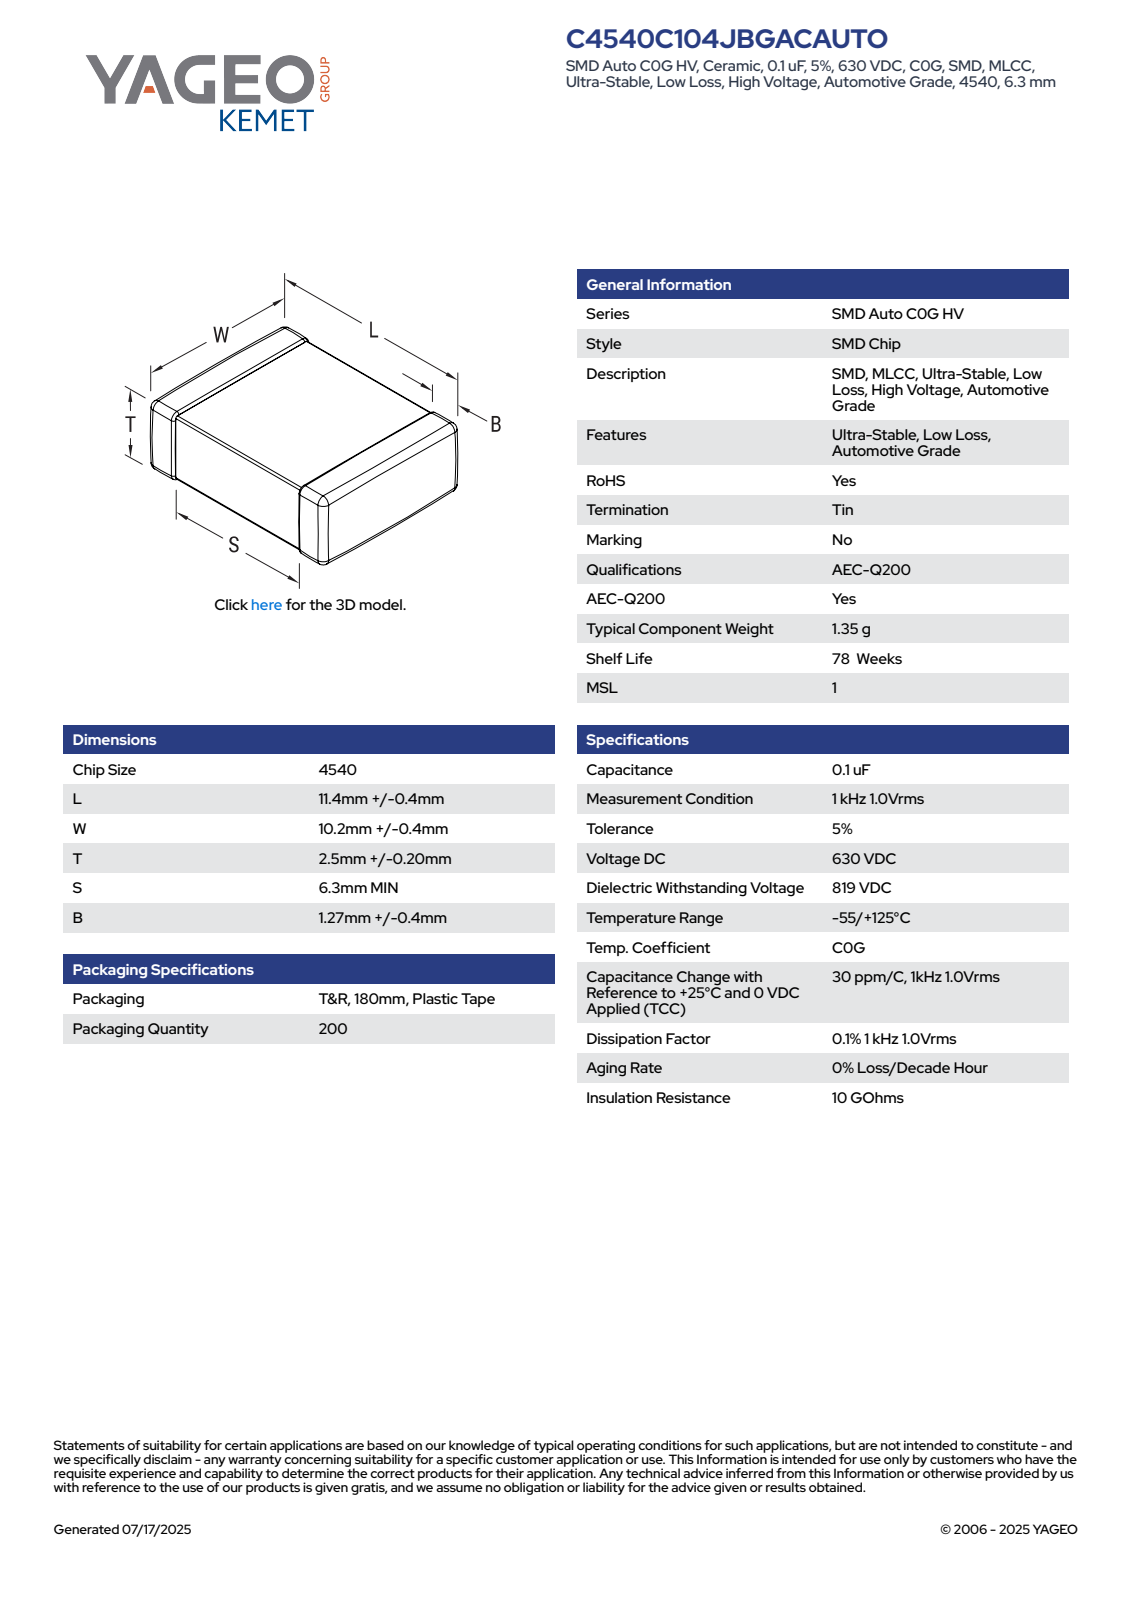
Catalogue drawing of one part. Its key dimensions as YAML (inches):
part_name: "CCS_CCSTDNOS_4540_L11.8W10.6T2.7B1.67"
step_written_by: "SolidWorks 2014 (AUTOMOTIVE_DESIGN)"
units: inches
bodies: {solids: 4, faces: 125, planar: 71, cylindrical: 38, other: 16}
overall_size: [0.465, 0.417, 0.106]
volume: 0.018
surface_area: 0.553
partial_cylinders:
  - {radius: 0.009, count: 24}
face_to_face_distances: [0.089, 0.098, 0.106, 0.465, 0.4, 0.409, 0.417, 0.206, 0.198, 0.202]
